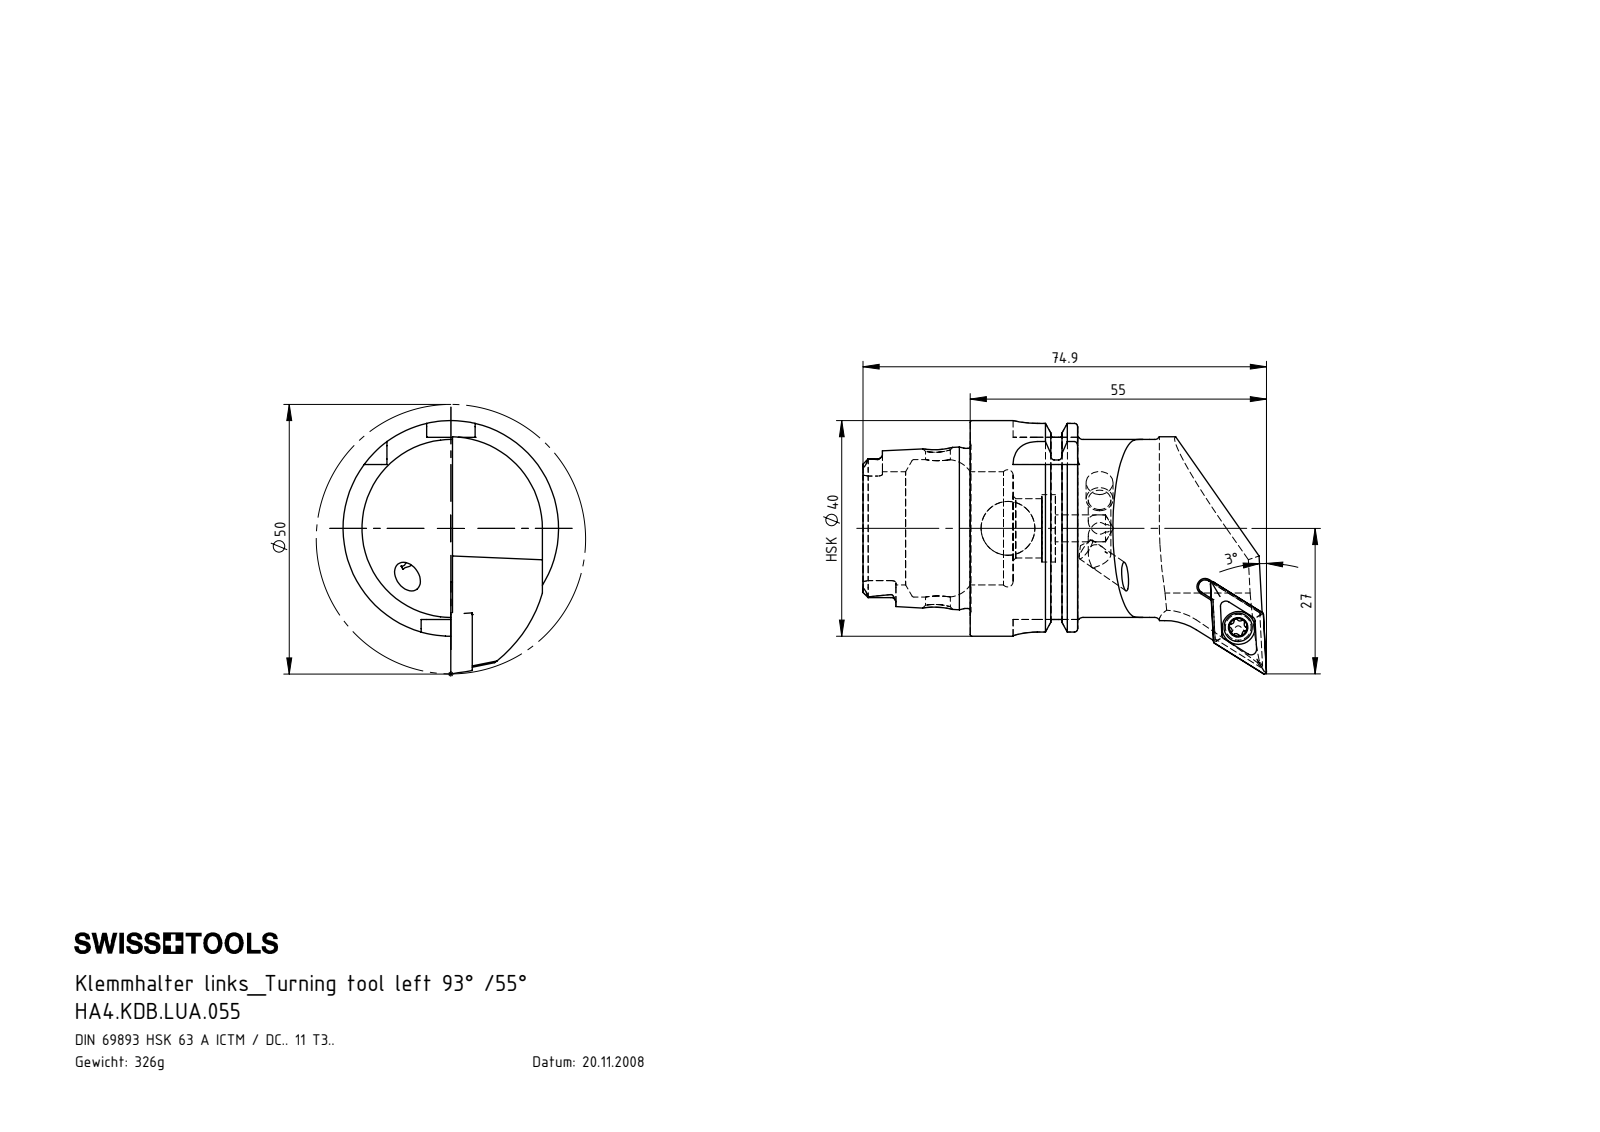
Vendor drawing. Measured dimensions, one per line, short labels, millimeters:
name: WCB-ER2.001.009_A; DCMT11T304; HA4-KDB.LUA.055_C_Fertigbearbeitung; HA4.KDB.LUA.055 (+1 more)
written by: SolidWorks 2017 (AUTOMOTIVE_DESIGN)
unit: mm
bodies: 5 solids, 314 faces (80 planar, 92 cylindrical, 142 other)
size: 74.9 × 47.01 × 40
volume: 41 296 mm³; area: 13 808 mm²
holes: 2× ⌀4.2, 2× ⌀5, 1× ⌀3.3, 1× ⌀4, 1× ⌀4.4, 1× ⌀4.6, 1× ⌀6.1, 1× ⌀10, 1× ⌀11, 1× ⌀12.5, 1× ⌀21, 1× ⌀25.5
bosses: 1× ⌀40, 1× ⌀34.75, 1× ⌀33, 1× ⌀29.71, 1× ⌀5.25, 1× ⌀5, 1× ⌀4
rounds: 6× R0.34, 6× R0.59, 6× R0.9, 4× R4.5, 2× R1.82, 2× R1.88, 1× R1.25, 1× R3
face distances: 7.95, 16.7, 19.95, 12, 13.03, 3.67, 19.9, 27.85, 39.85, 35.7
hole spacings: 46.51, 46.61
